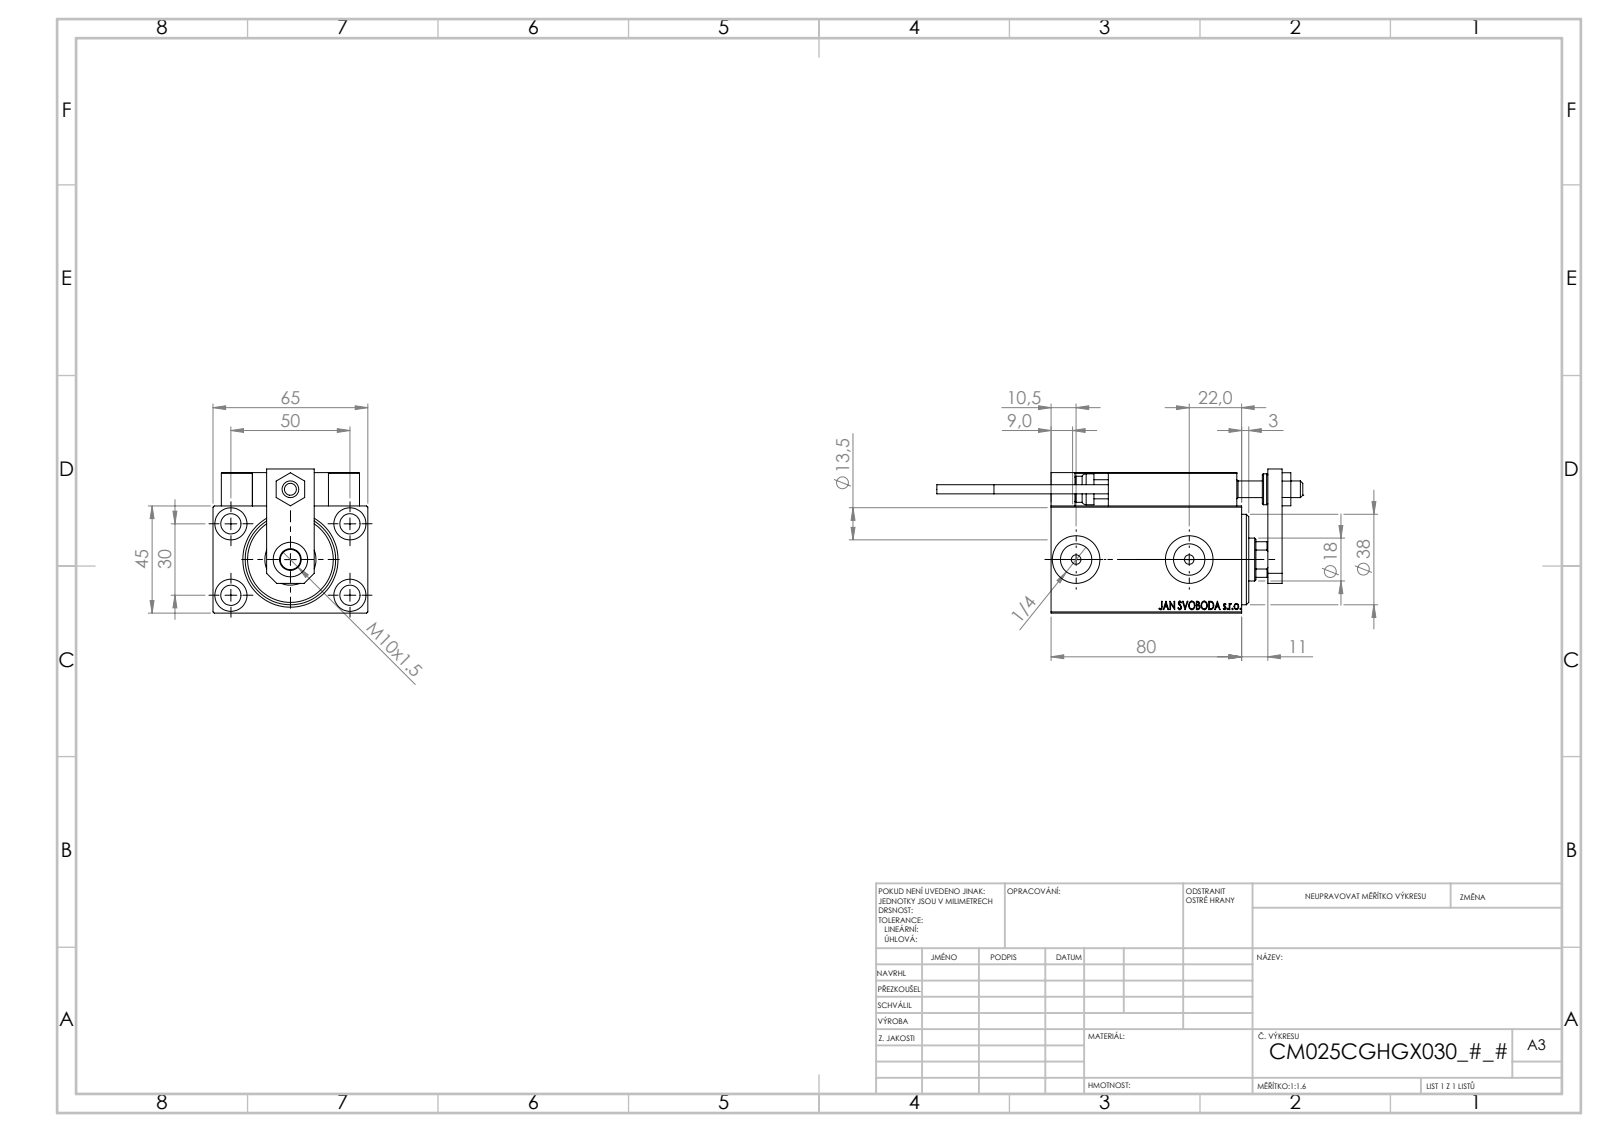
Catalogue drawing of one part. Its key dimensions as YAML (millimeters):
part_name: "V450CM_C_Body; V450CM_C_VCP; KONCOVKA; V450CM_VC_B (+7 more)"
step_written_by: "SolidWorks 2019 (CONFIG_CONTROL_DESIGN)"
units: millimeters
bodies: {solids: 23, faces: 1282, planar: 560, cylindrical: 188, other: 534}
overall_size: [153.7, 65, 60.5]
volume: 248224
surface_area: 74049
round_holes:
  - {diameter: 4, count: 6}
  - {diameter: 8, count: 5}
  - {diameter: 8.5, count: 5}
  - {diameter: 3.2, count: 4}
  - {diameter: 13.5, count: 4}
  - {diameter: 5, count: 2}
  - {diameter: 13.16, count: 2}
  - {diameter: 20, count: 2}
  - {diameter: 7, count: 1}
  - {diameter: 14.5, count: 1}
  - {diameter: 18, count: 1}
  - {diameter: 21.5, count: 1}
round_bosses_or_shafts:
  - {diameter: 5, count: 2}
  - {diameter: 3.8, count: 2}
  - {diameter: 13, count: 1}
  - {diameter: 11, count: 1}
partial_cylinders:
  - {radius: 0.3, count: 30}
  - {radius: 3, count: 2}
  - {radius: 8.5, count: 1}
face_to_face_distances: [45, 65, 14, 59, 6, 3, 13, 3.5, 5, 7]
hole_center_spacings: [29.15, 11.37, 20, 28.9, 29.59, 29.69, 30, 32.06]
